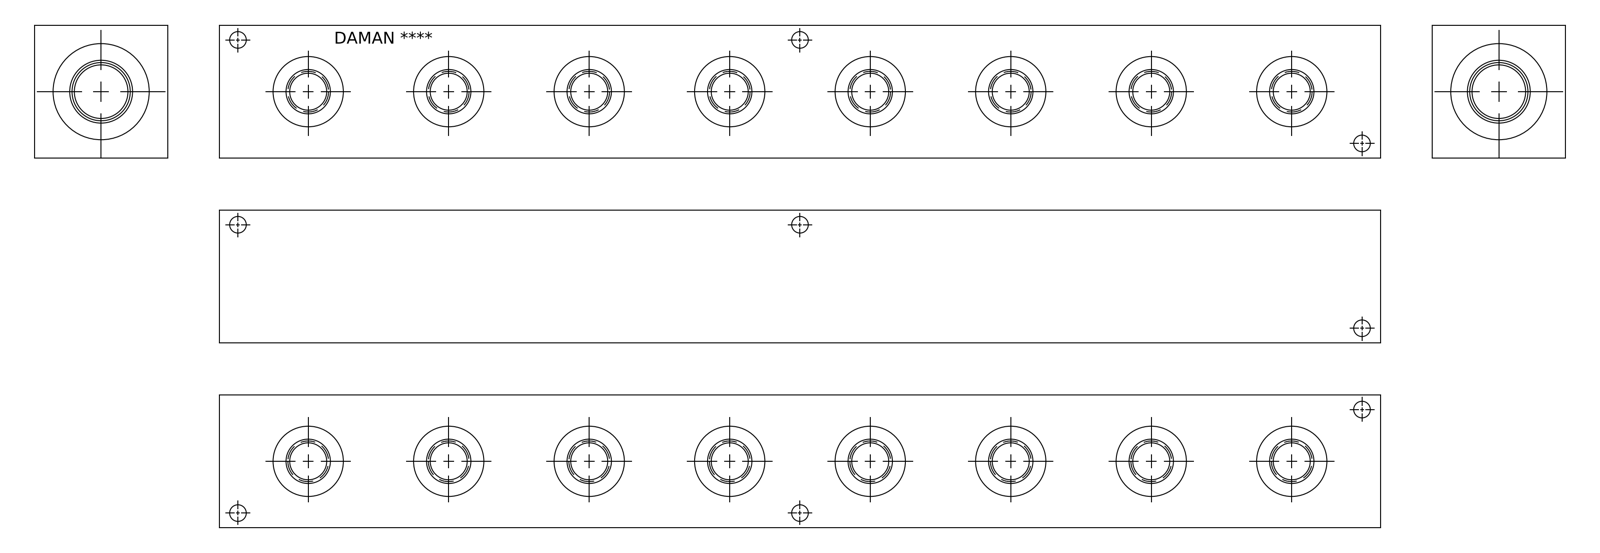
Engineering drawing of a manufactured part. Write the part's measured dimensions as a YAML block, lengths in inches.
part_name: "Part_+H1800808S_3D"
step_written_by: "Autodesk Inventor 2019 (AUTOMOTIVE_DESIGN)"
units: inches
bodies: {solids: 1, faces: 530, planar: 246, cylindrical: 98, other: 186}
overall_size: [19.625, 2.25, 2.25]
volume: 90.01
surface_area: 236.7
round_holes:
  - {diameter: 0.689, count: 8}
  - {diameter: 0.75, count: 8}
  - {diameter: 0.758, count: 8}
  - {diameter: 1.206, count: 8}
  - {diameter: 0.281, count: 6}
  - {diameter: 0.625, count: 6}
  - {diameter: 0.906, count: 1}
  - {diameter: 0.981, count: 1}
  - {diameter: 1.063, count: 1}
  - {diameter: 1.063, count: 1}
  - {diameter: 1.08, count: 1}
  - {diameter: 1.655, count: 1}
face_to_face_distances: [2.25, 0.031, 2.219, 2.188, 19.625, 19.594, 19.563, 0.593, 1.657, 0.562]
hole_center_spacings: [4.75, 2.375, 7.125, 9.5, 2.375, 11.875, 1.476, 3.668]
